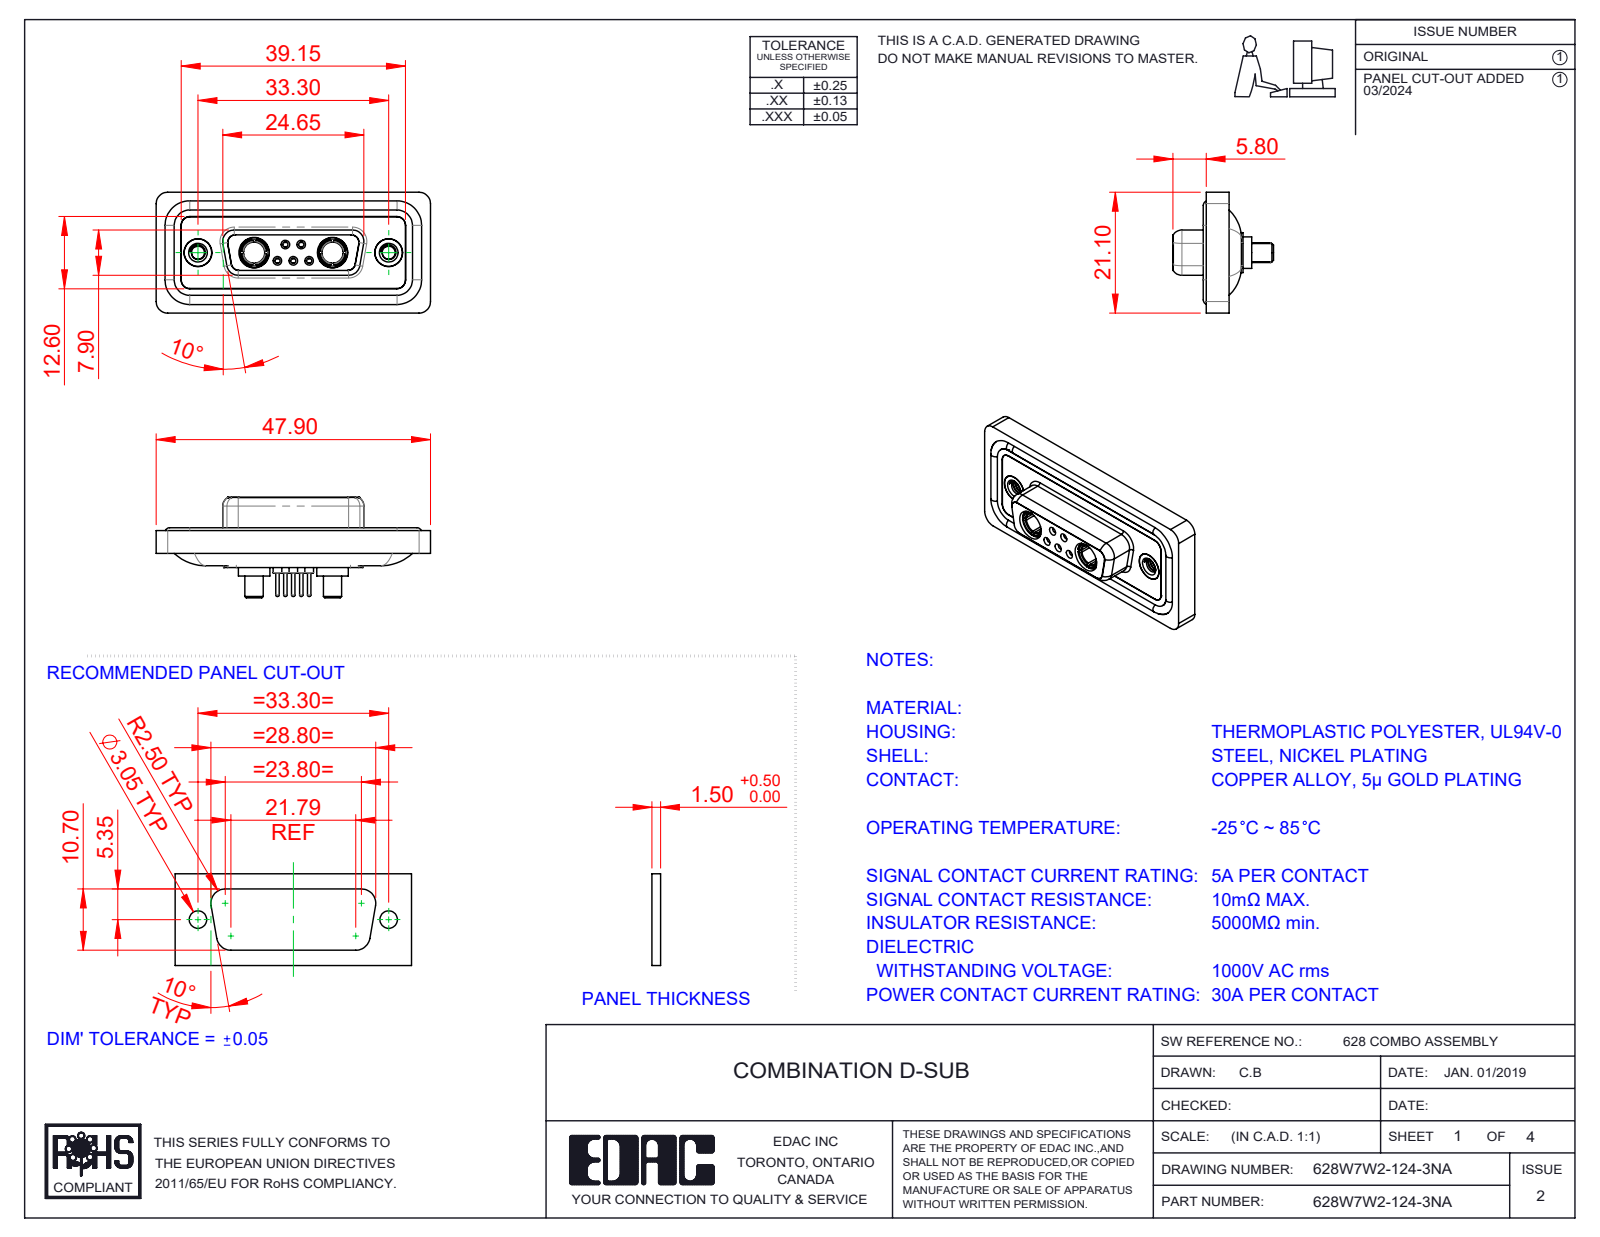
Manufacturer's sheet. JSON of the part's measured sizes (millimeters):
{"part_name": "Power Socket_30A S; 628Combo Threaded Rivet_A; 628Combo Waterproof Housing_15 Contacts; 628Combo Shell Rear_15 Contacts (+5 more)", "step_written_by": "SolidWorks 2023 (CONFIG_CONTROL_DESIGN)", "units": "millimeters", "bodies": {"solids": 16, "faces": 807, "planar": 238, "cylindrical": 331, "other": 238}, "overall_size": [47.9, 21.1, 17.55], "volume_mm3": 6093, "surface_area_mm2": 9892, "round_holes": [[0.9, 5], [1.1, 5], [1.5, 5], [2, 5], [4.85, 4], [1.6, 3], [1.7, 2], [2.26, 2], [3.7, 2], [4, 2], [4.05, 2], [5, 2]], "round_bosses_or_shafts": [[1.6, 6], [2.2, 5], [0.6, 5], [5.5, 2], [5.2, 2], [4.96, 2], [4.95, 2], [4.8, 2]], "partial_cylinders_radius": [[1.5, 22], [2, 20], [1.35, 12], [1.6, 8], [0.25, 4], [0.5, 4], [0.6, 4], [0.65, 4]], "face_to_face_distances": [0.4, 1.8, 1.6, 0.5, 2.9, 7.45, 1.1, 5.65, 6.6, 7.05], "hole_center_spacings": [3.16, 2.77, 9.8, 23.5, 4.31, 4.33, 5.03, 5.04]}
